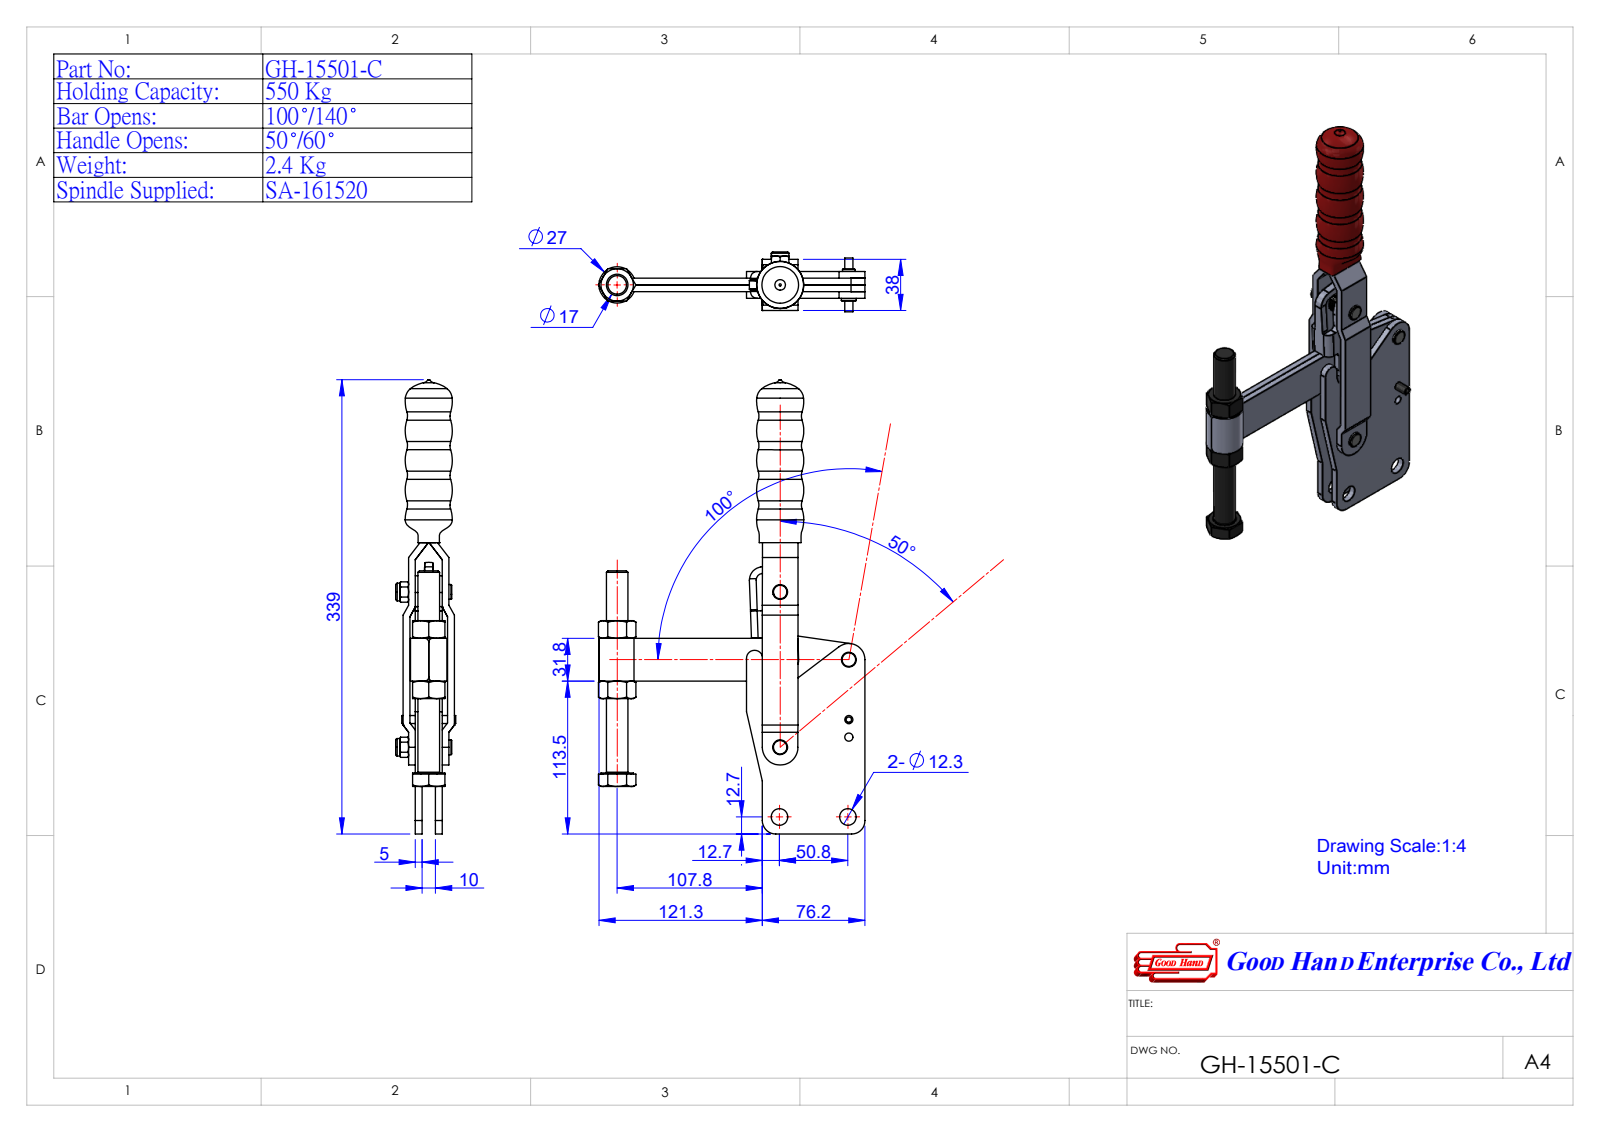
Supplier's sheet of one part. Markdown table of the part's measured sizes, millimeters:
| quantity | value |
| --- | --- |
| part name | Group4^GH-15501-C(簡化)-1; Group3^GH-15501-C(簡化)-1; Group1^GH-15501-C(簡化)-1; Group2^GH-15501-C(簡化)-1 (+2 more) |
| STEP written by | SolidWorks 2016 (AUTOMOTIVE_DESIGN) |
| units | millimeters |
| bodies | 5 solids, 332 faces (124 planar, 98 cylindrical, 110 other) |
| overall size | 337.19 × 197.86 × 41.44 |
| volume | 374 169 mm³ |
| surface area | 124 139 mm² |
| round holes (diameter × count) | 7.5 × 4, 12.3 × 2, 6 × 1, 14 × 1, 16 × 1, 17 × 1 |
| round bosses / shafts (diameter × count) | 10 × 2, 9.5 × 2, 9.45 × 2, 27 × 1, 24 × 1, 7.5 × 1, 6 × 1 |
| partial cylindrical surfaces (radius × count) | 12 × 3, 3 × 2, 10 × 2, 11 × 2, 6 × 1, 13.2 × 1, 15 × 1 |
| main face-to-face distances | 5, 15, 10, 20, 24, 9, 29, 4, 14, 33 |
| hole center spacings | 49.25, 50.23, 50.8, 51.55, 51.7, 57.48, 59.22, 65.02 |
